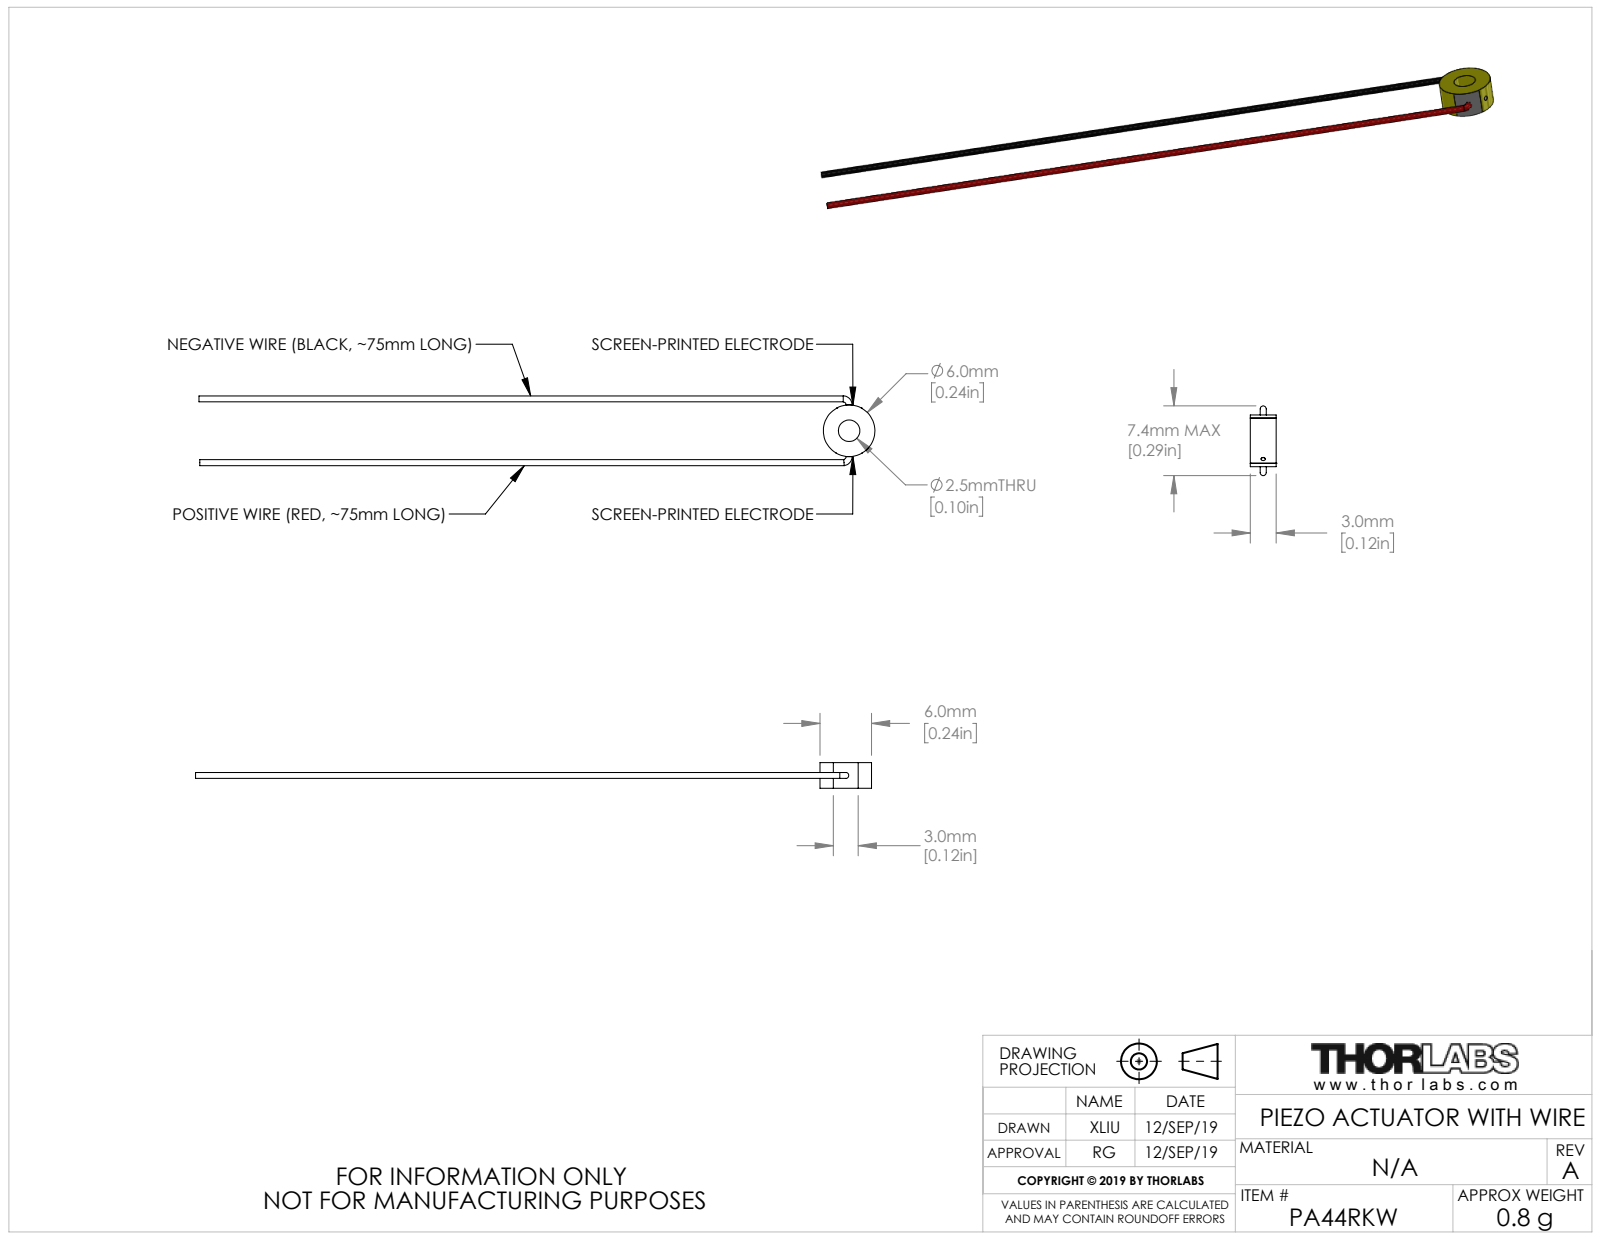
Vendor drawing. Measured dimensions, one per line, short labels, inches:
name: CTN014427
written by: SolidWorks 2018 (AUTOMOTIVE_DESIGN)
unit: in
bodies: 3 solids, 28 faces (9 planar, 12 cylindrical, 7 other)
size: 3.098 × 0.319 × 0.118
volume: 0.008 in³; area: 0.718 in²
holes: 1× ⌀0.098
bosses: 2× ⌀0.028
rounds: 1× R0.118, 1× R0.119
face distances: 0.118, 0.237
